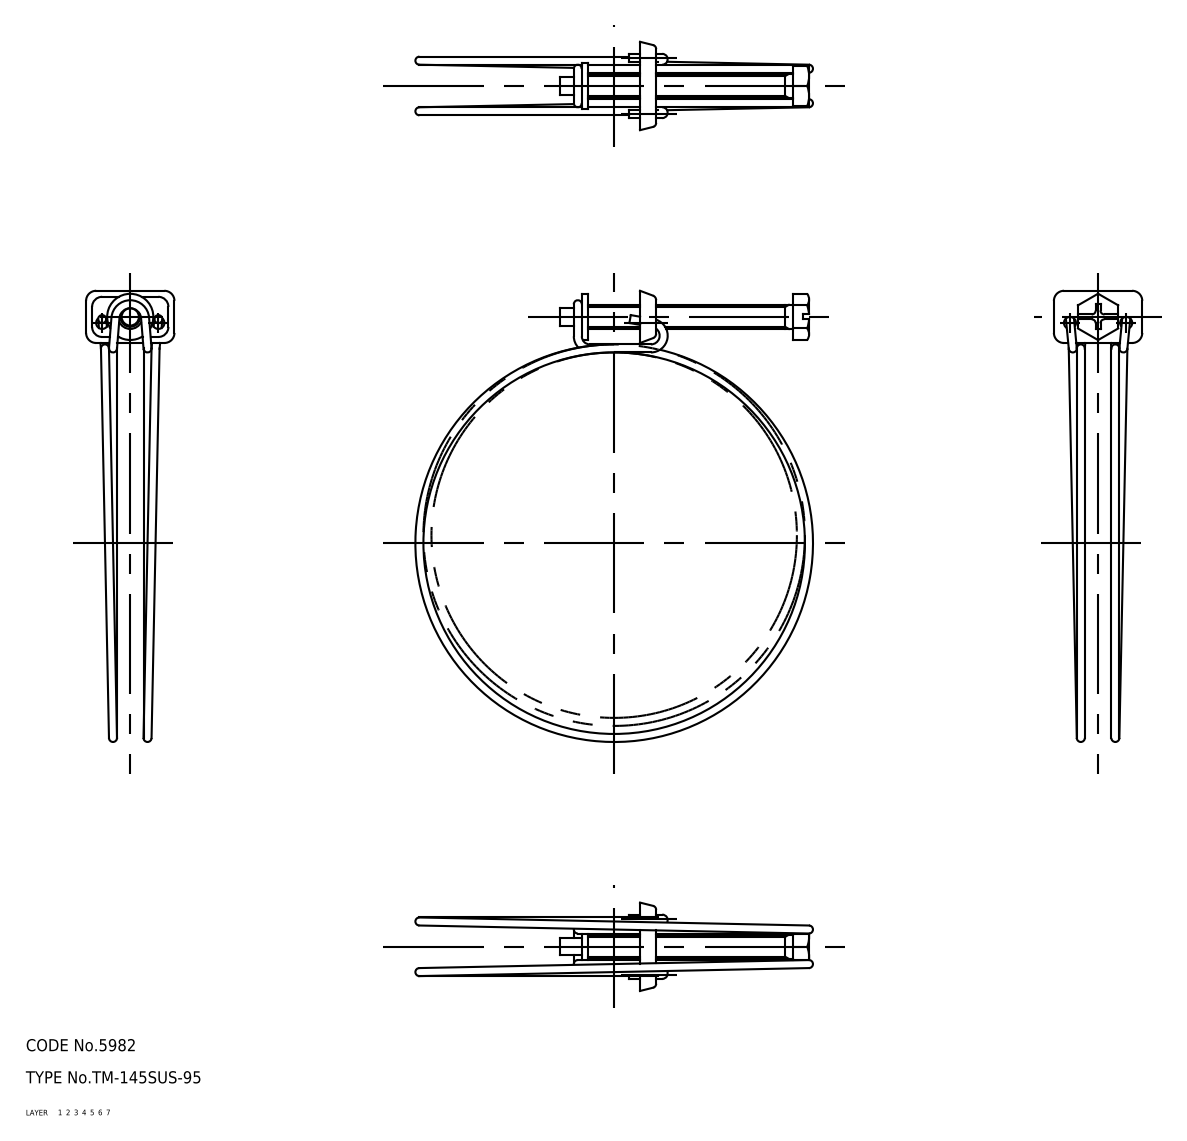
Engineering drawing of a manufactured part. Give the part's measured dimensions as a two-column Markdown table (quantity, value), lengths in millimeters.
| quantity | value |
| --- | --- |
| part name | screw; holder; band; TM_145SUS_95_23134_36 |
| STEP written by | CADfix (AUTOMOTIVE_DESIGN) |
| units | millimeters |
| bodies | 3 solids, 119 faces (0 planar, 0 cylindrical, 119 other) |
| overall size | 112.35 × 99 × 22 |
| volume | 4 703 mm³ |
| surface area | 6 805 mm² |
